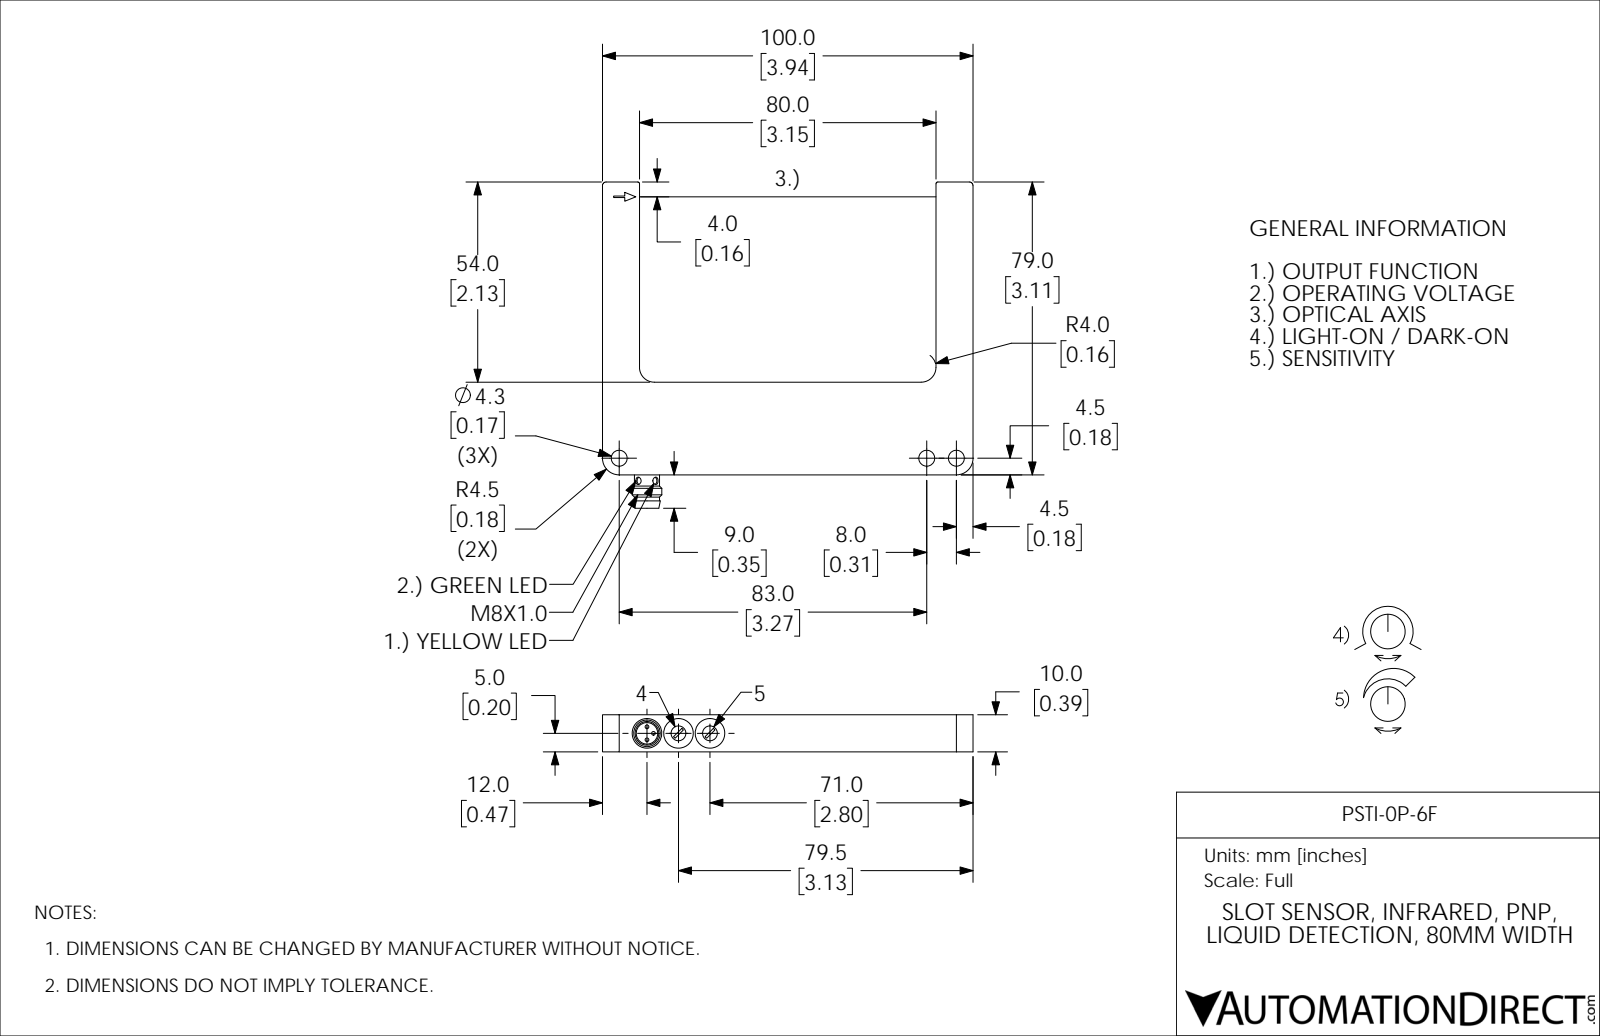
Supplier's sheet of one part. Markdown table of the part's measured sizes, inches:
| quantity | value |
| --- | --- |
| part name | PSTI-0P-6F |
| STEP written by | SolidWorks 2017 (AUTOMOTIVE_DESIGN) |
| units | inches |
| bodies | 1 solid, 74 faces (38 planar, 30 cylindrical, 6 other) |
| overall size | 3.937 × 3.465 × 0.394 |
| volume | 2.17 in³ |
| surface area | 19.26 in² |
| round holes (diameter × count) | 0.169 × 3, 0.079 × 2, 0.157 × 2, 0.315 × 2, 0.228 × 1 |
| round bosses / shafts (diameter × count) | 0.039 × 3, 0.315 × 1, 0.267 × 1 |
| partial cylindrical surfaces (radius × count) | 0.02 × 2, 0.039 × 2, 0.063 × 2, 0.157 × 2, 0.177 × 2 |
| main face-to-face distances | 0.394, 3.543, 3.937, 0.984, 3.15, 2.126, 3.11, 3.106, 0.98, 0.157 |
| hole center spacings | 0.335, 0.315, 0.669, 3.268, 3.583 |
